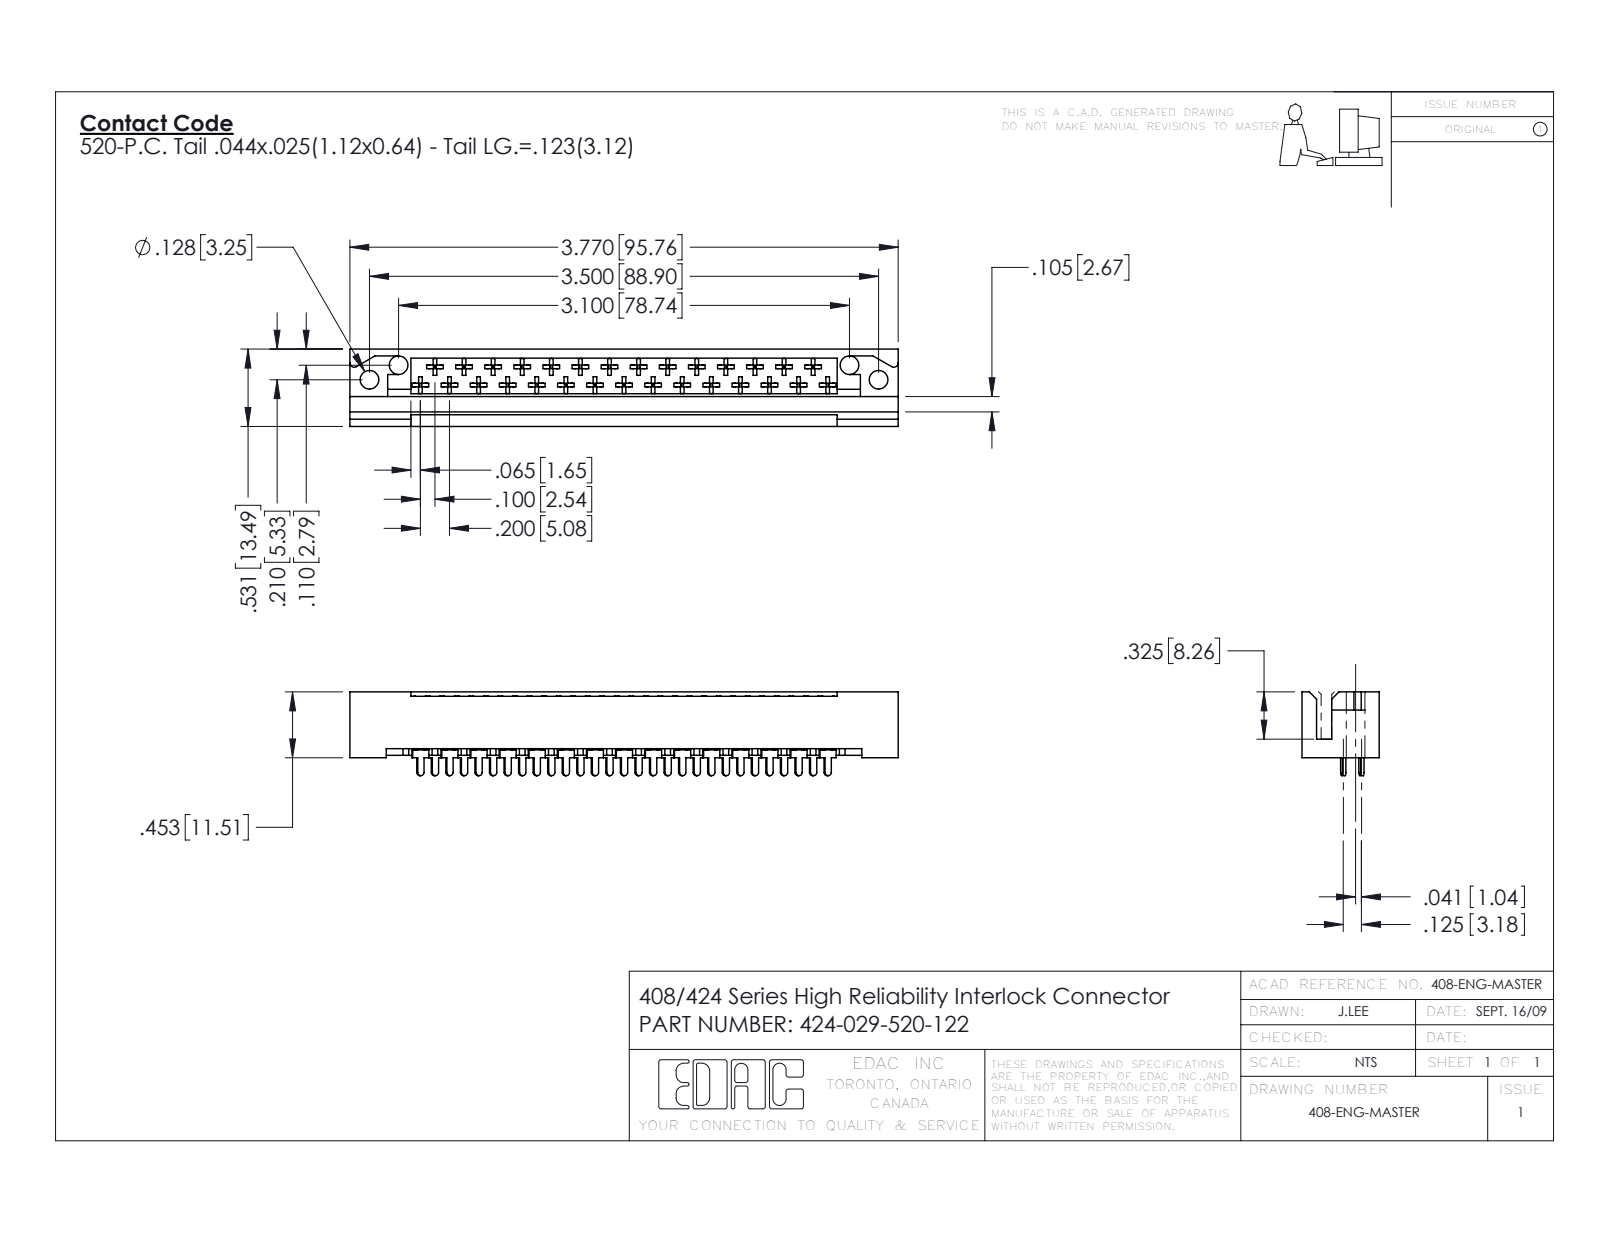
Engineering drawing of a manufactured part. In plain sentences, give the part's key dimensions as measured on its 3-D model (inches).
The part is named "408-290-001_408-290-120; 424-029-520-122; 424 Part_029". Its 3-D file was written by "SolidWorks 2016 (CONFIG_CONTROL_DESIGN)". It is 30 solids with 1657 faces: 1264 planar, 277 cylindrical and 116 other. Overall it measures 3.77 by 0.576 by 0.531 inches. Its volume is 0.602 cubic inches and its surface area 19.64 square inches. Round holes: 4 of diameter 0.128. Partial cylindrical surfaces (rounded edges, fillets, slot ends): 174 of radius 0.01, 31 of radius 0.02, 29 of radius 0.022, 2 of radius 0.03. The main face-to-face distances are 0.1, 0.296, 0.531, 0.025, 0.125, 0.431, 0.259, 0.172, 0.272, 0.235. The hole center spacings are 0.224, 3.302, 3.1, 3.5.
